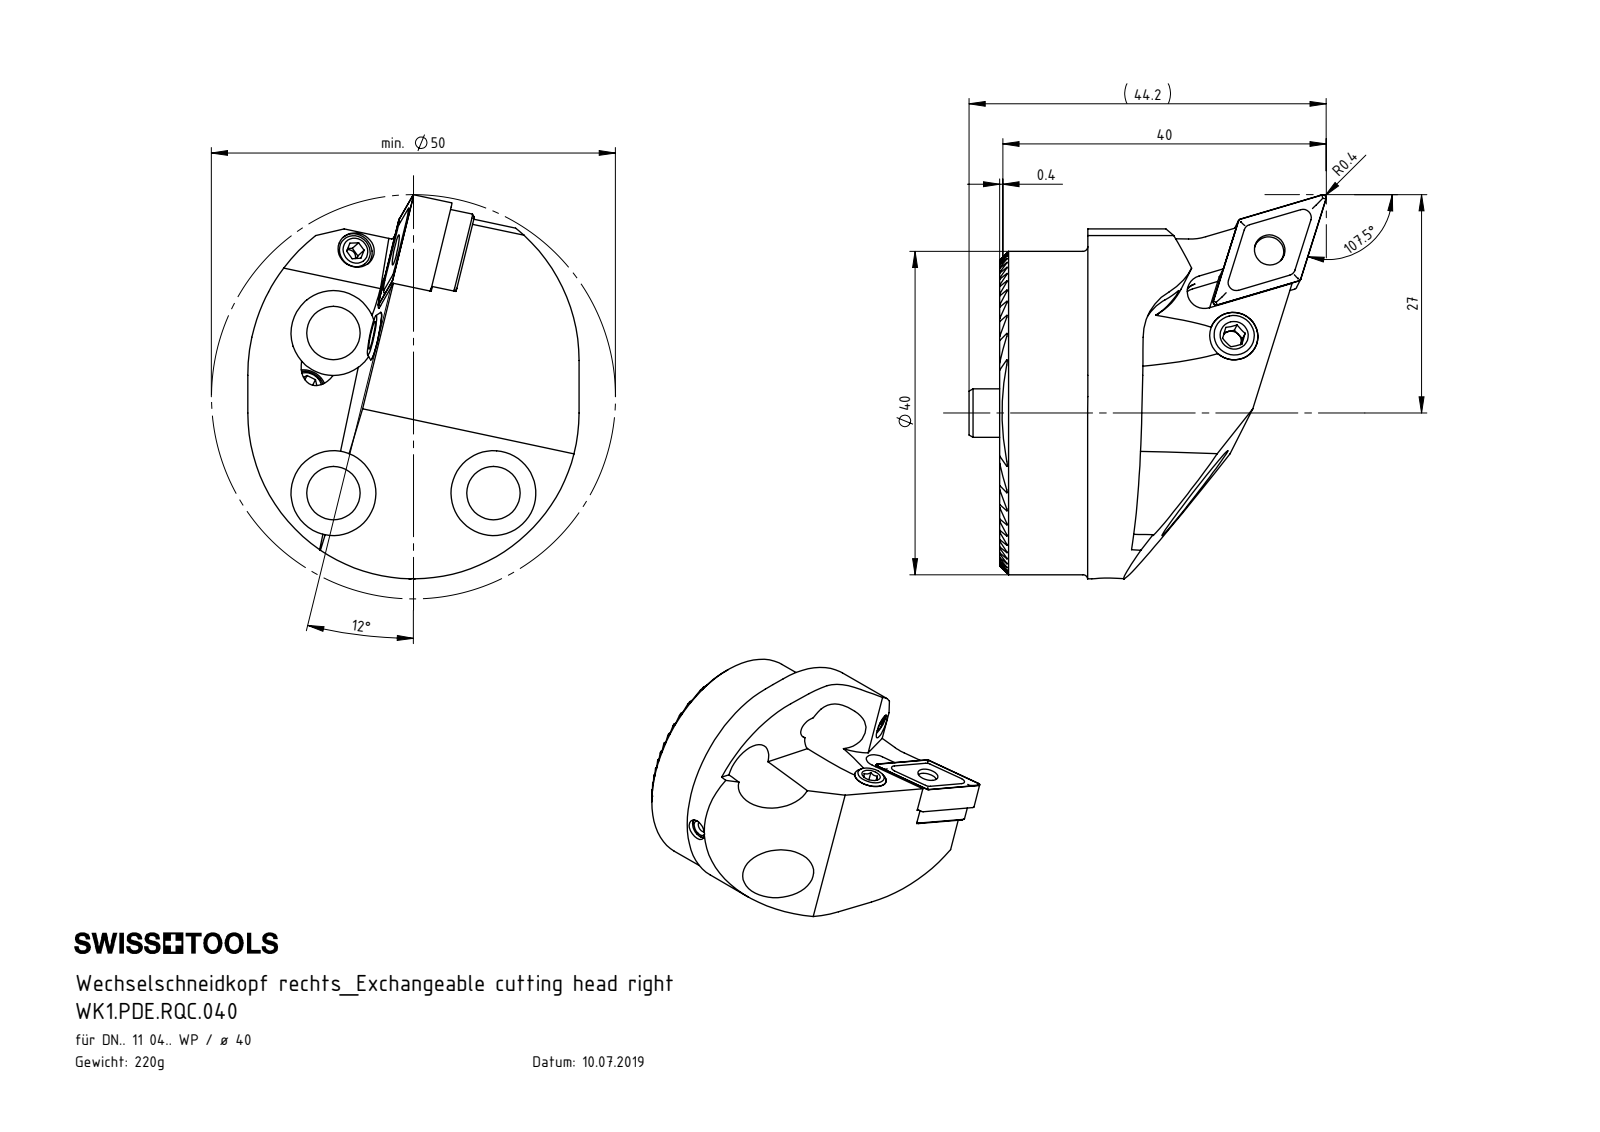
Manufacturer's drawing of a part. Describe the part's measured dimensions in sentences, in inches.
The part is named "KVT_MB_600_040; WDE-ER4.101.017_A; WK2-ER1.001.012_A_Fertigbearbeitung; WDE-ER1.101.000 (+6 more)". Its 3-D file was written by "SolidWorks 2017 (AUTOMOTIVE_DESIGN)". It is 15 solids with 506 faces: 279 planar, 118 cylindrical and 109 other. Overall it measures 1.87 by 1.741 by 1.614 inches. Its volume is 1.739 cubic inches and its surface area 20.7 square inches. Round holes: 5 of diameter 0.13, 3 of diameter 0.118, 3 of diameter 0.26, 3 of diameter 0.413, 2 of diameter 0.067, 2 of diameter 0.157, 2 of diameter 0.177, 1 of diameter 0.15, 1 of diameter 0.165, 1 of diameter 0.189, 1 of diameter 0.197, 1 of diameter 0.252. Round bosses or shafts: 5 of diameter 0.157, 2 of diameter 0.236, 1 of diameter 1.575, 1 of diameter 0.232, 1 of diameter 0.113. Partial cylindrical surfaces (rounded edges, fillets, slot ends): 26 of radius 0.005, 8 of radius 0.016, 5 of radius 0.083, 2 of radius 0.276, 1 of radius 0.072, 1 of radius 0.073, 1 of radius 0.089, 1 of radius 0.093. The main face-to-face distances are 0.051, 0.102, 0.154, 0.511, 0.205, 0.46, 0.358, 0.409, 0.307, 0.256. The hole center spacings are 0.551, 0.78, 0.465, 1.102.
